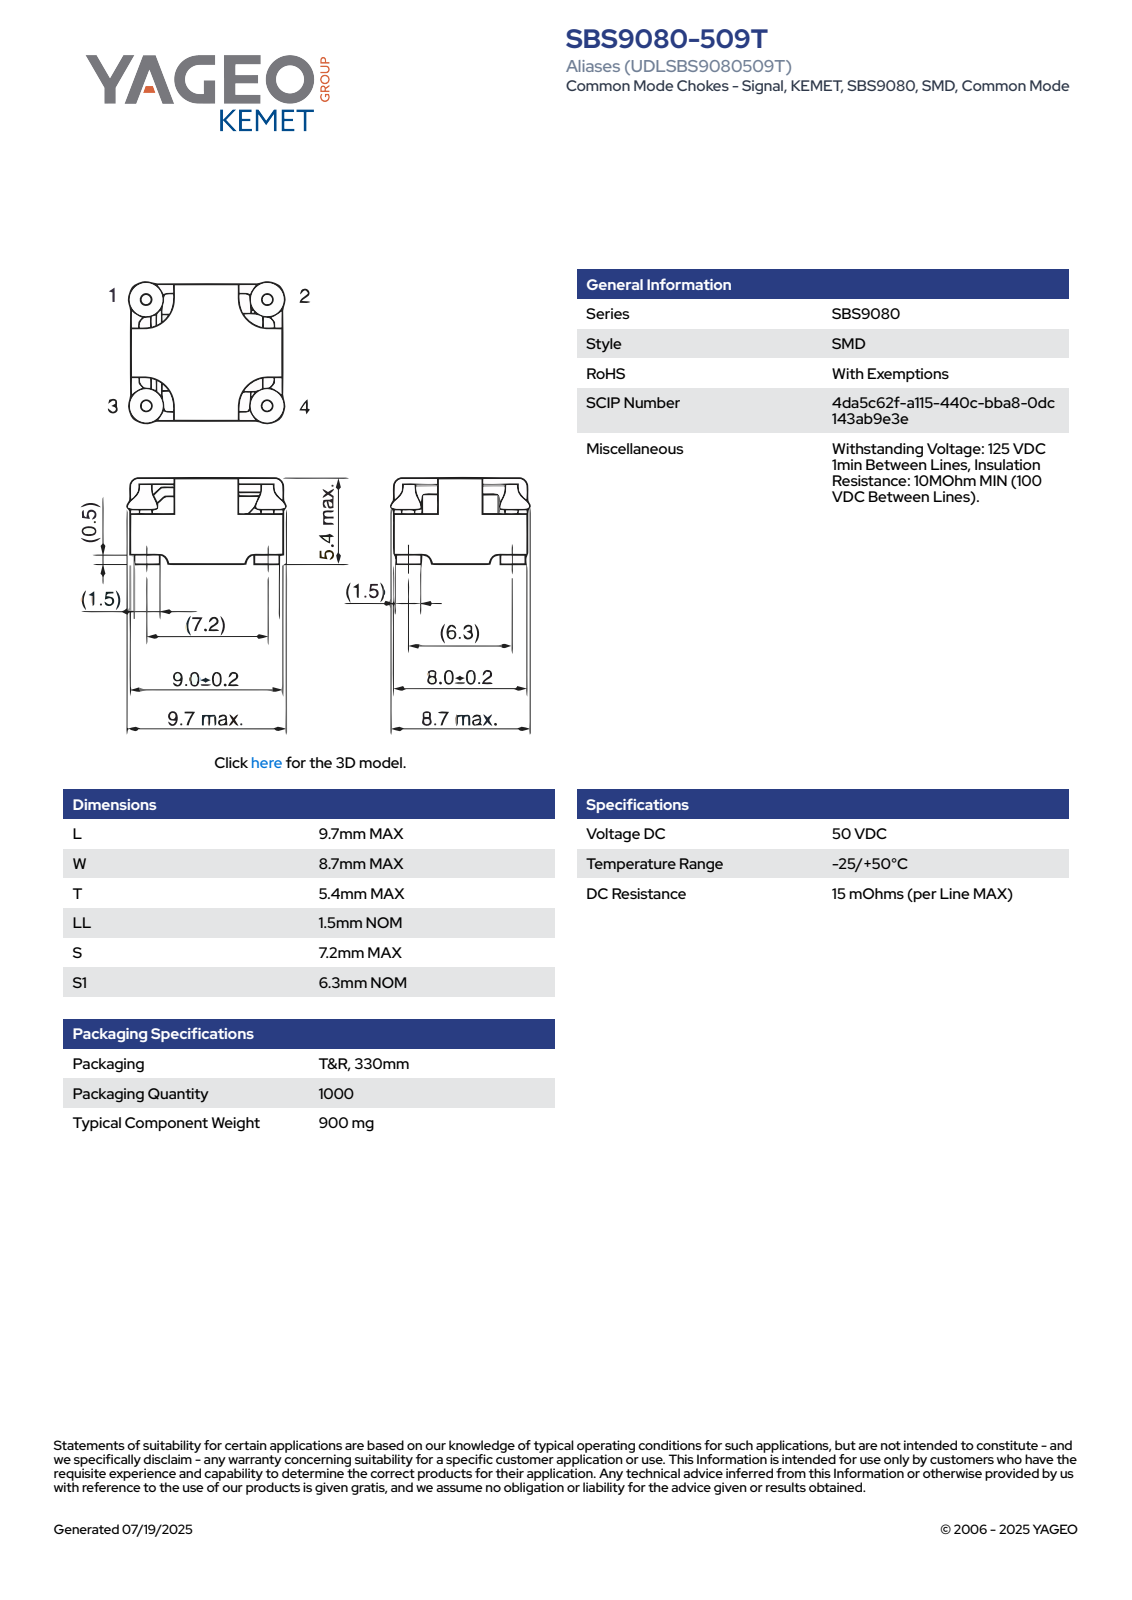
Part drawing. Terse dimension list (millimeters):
name: IFC_NT_SBS9080_L9.7W8.7T5.4
written by: SolidWorks 2014 (AUTOMOTIVE_DESIGN)
unit: mm
bodies: 1 solid, 146 faces (80 planar, 36 cylindrical, 30 other)
size: 9.7 × 8.7 × 5.41
volume: 369 mm³; area: 360 mm²
bosses: 4× ⌀1.8, 4× ⌀1.5
rounds: 8× R0.2, 4× R1.79, 4× R2.09
face distances: 5.4, 8.2, 9.2, 3.4, 2, 0.5, 4.9, 2.9, 2.01, 5.41
